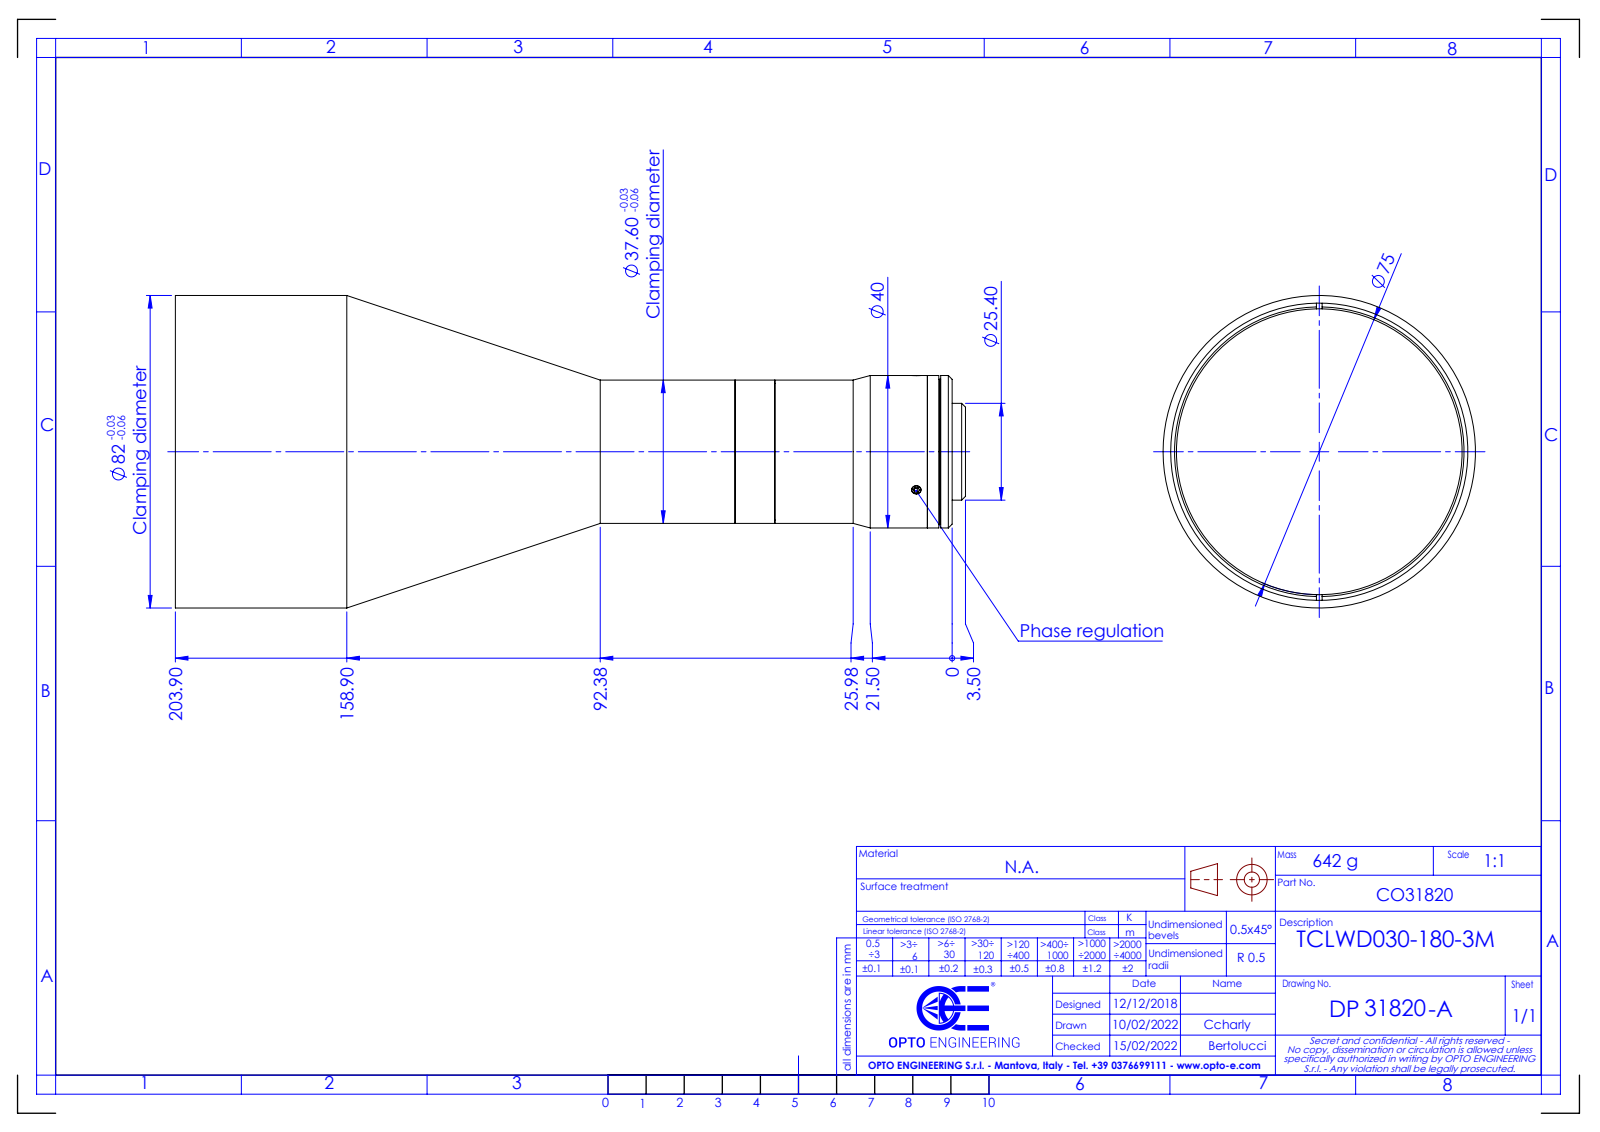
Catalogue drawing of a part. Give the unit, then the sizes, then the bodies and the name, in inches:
Units: inches
Overall size (bounding box): 8.165 × 3.228 × 3.228
Round holes (diameter × count): ⌀0.098 ×1, ⌀0.886 ×1, ⌀1.004 ×1, ⌀1.26 ×1, ⌀2.953 ×1, ⌀3.071 ×1
Round bosses / shafts (diameter × count): ⌀3.228 ×1, ⌀1.575 ×1, ⌀1.48 ×1, ⌀1 ×1
Main face-to-face distances: 0.138, 0.118, 0.02, 7.89, 7.909, 8.028, 0.256, 7.772, 6.198, 1.574
Bodies: 0 solids, 85 faces (38 planar, 28 cylindrical, 19 other)
Part name (STEP PRODUCT): DP31820-A_TCLWD030-180-3M
STEP written by: SolidWorks 2021 (CONFIG_CONTROL_DESIGN)
